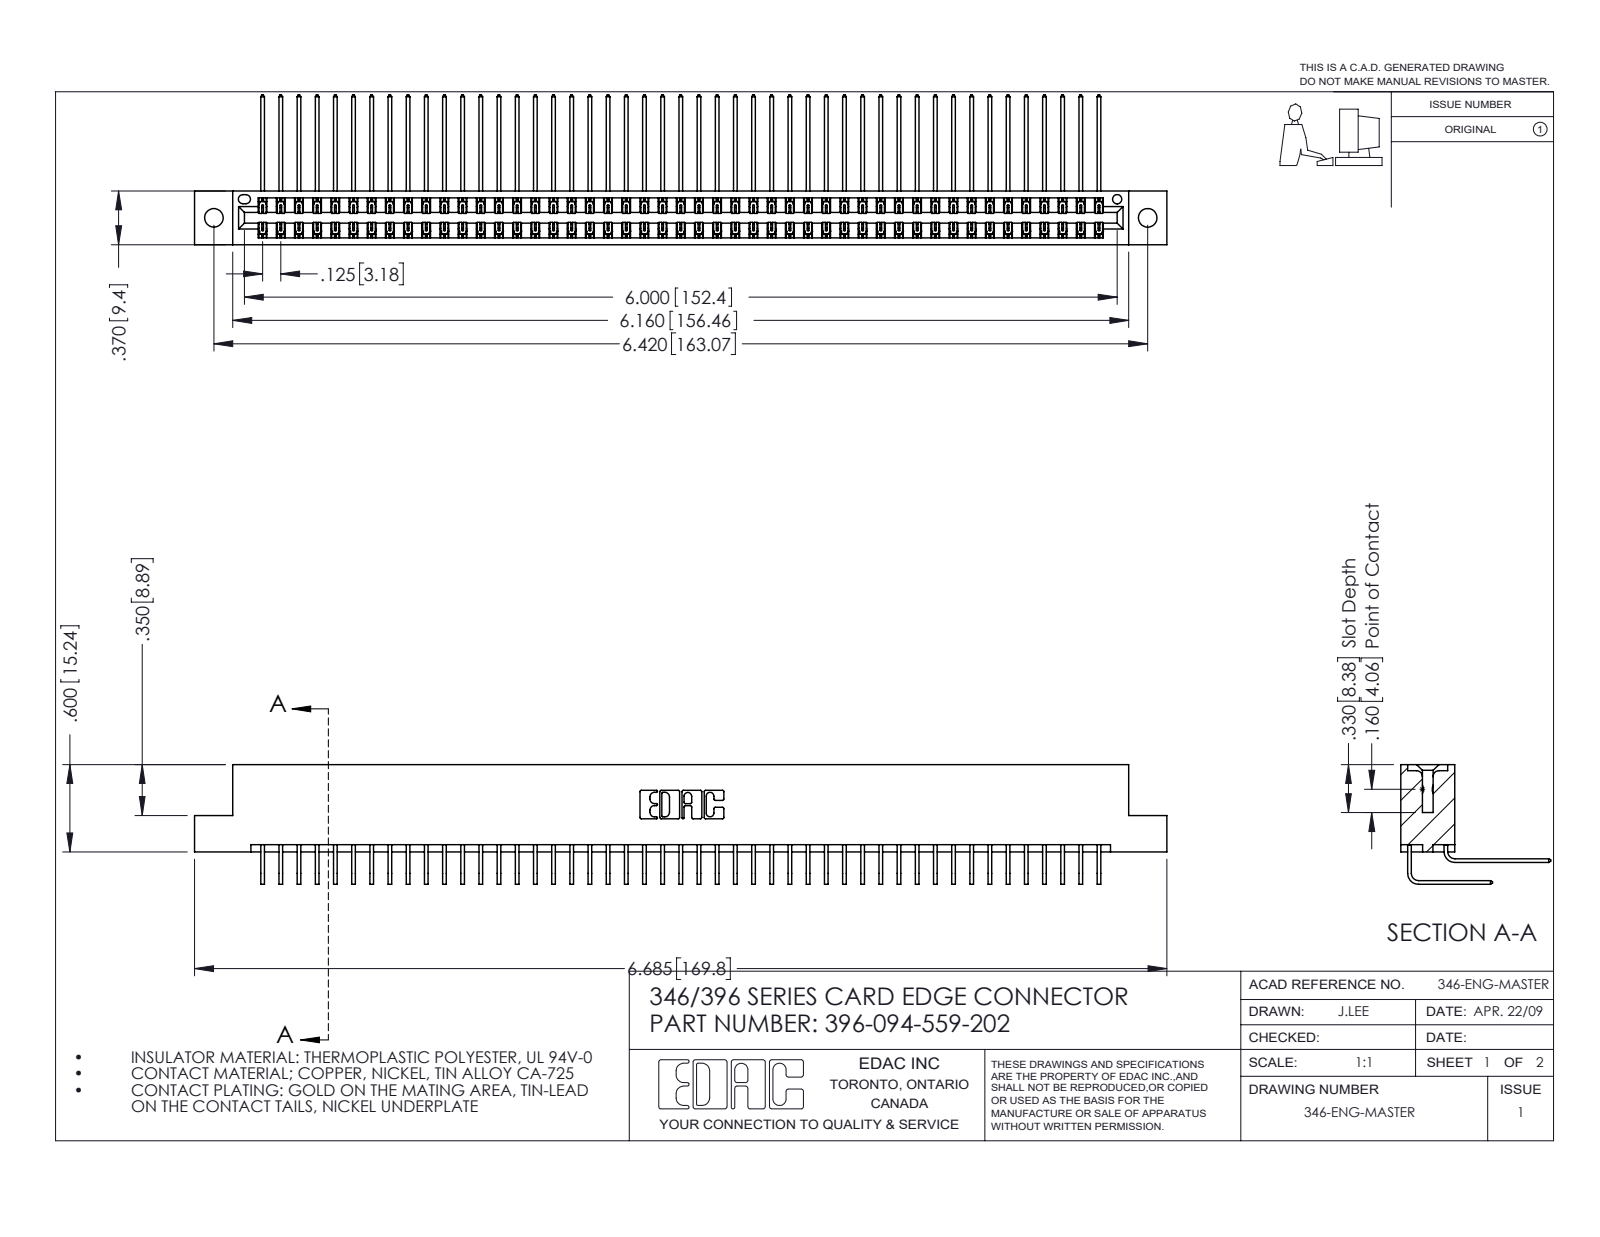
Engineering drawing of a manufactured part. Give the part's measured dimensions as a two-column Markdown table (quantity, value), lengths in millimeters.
| quantity | value |
| --- | --- |
| part name | 396-094-559-202; 345-292-001_558 559 Tail - 1; 345-292-001_559 Tail - 2; 346 Part_Flush Mounting Lugs - 0.128 Dia |
| STEP written by | SolidWorks 2016 (CONFIG_CONTROL_DESIGN) |
| units | millimeters |
| bodies | 95 solids, 5198 faces (3554 planar, 1644 cylindrical, 0 other) |
| overall size | 169.8 × 26.2 × 20.9 |
| volume | 17 110 mm³ |
| surface area | 25 920 mm² |
| round holes (diameter × count) | 3.3 × 2, 1.6 × 1 |
| partial cylindrical surfaces (radius × count) | 0.2 × 141, 0.3 × 22, 0.2 × 6, 0.8 × 6, 0.7 × 3, 0.4 × 2, 0.6 × 2, 0.6 × 2 |
| main face-to-face distances | 1.2, 8.2, 0.6, 9.4, 6.4, 1.8, 7.6, 7, 3.8, 5.6 |
| hole center spacings | 6.2, 157.8, 163.1 |
